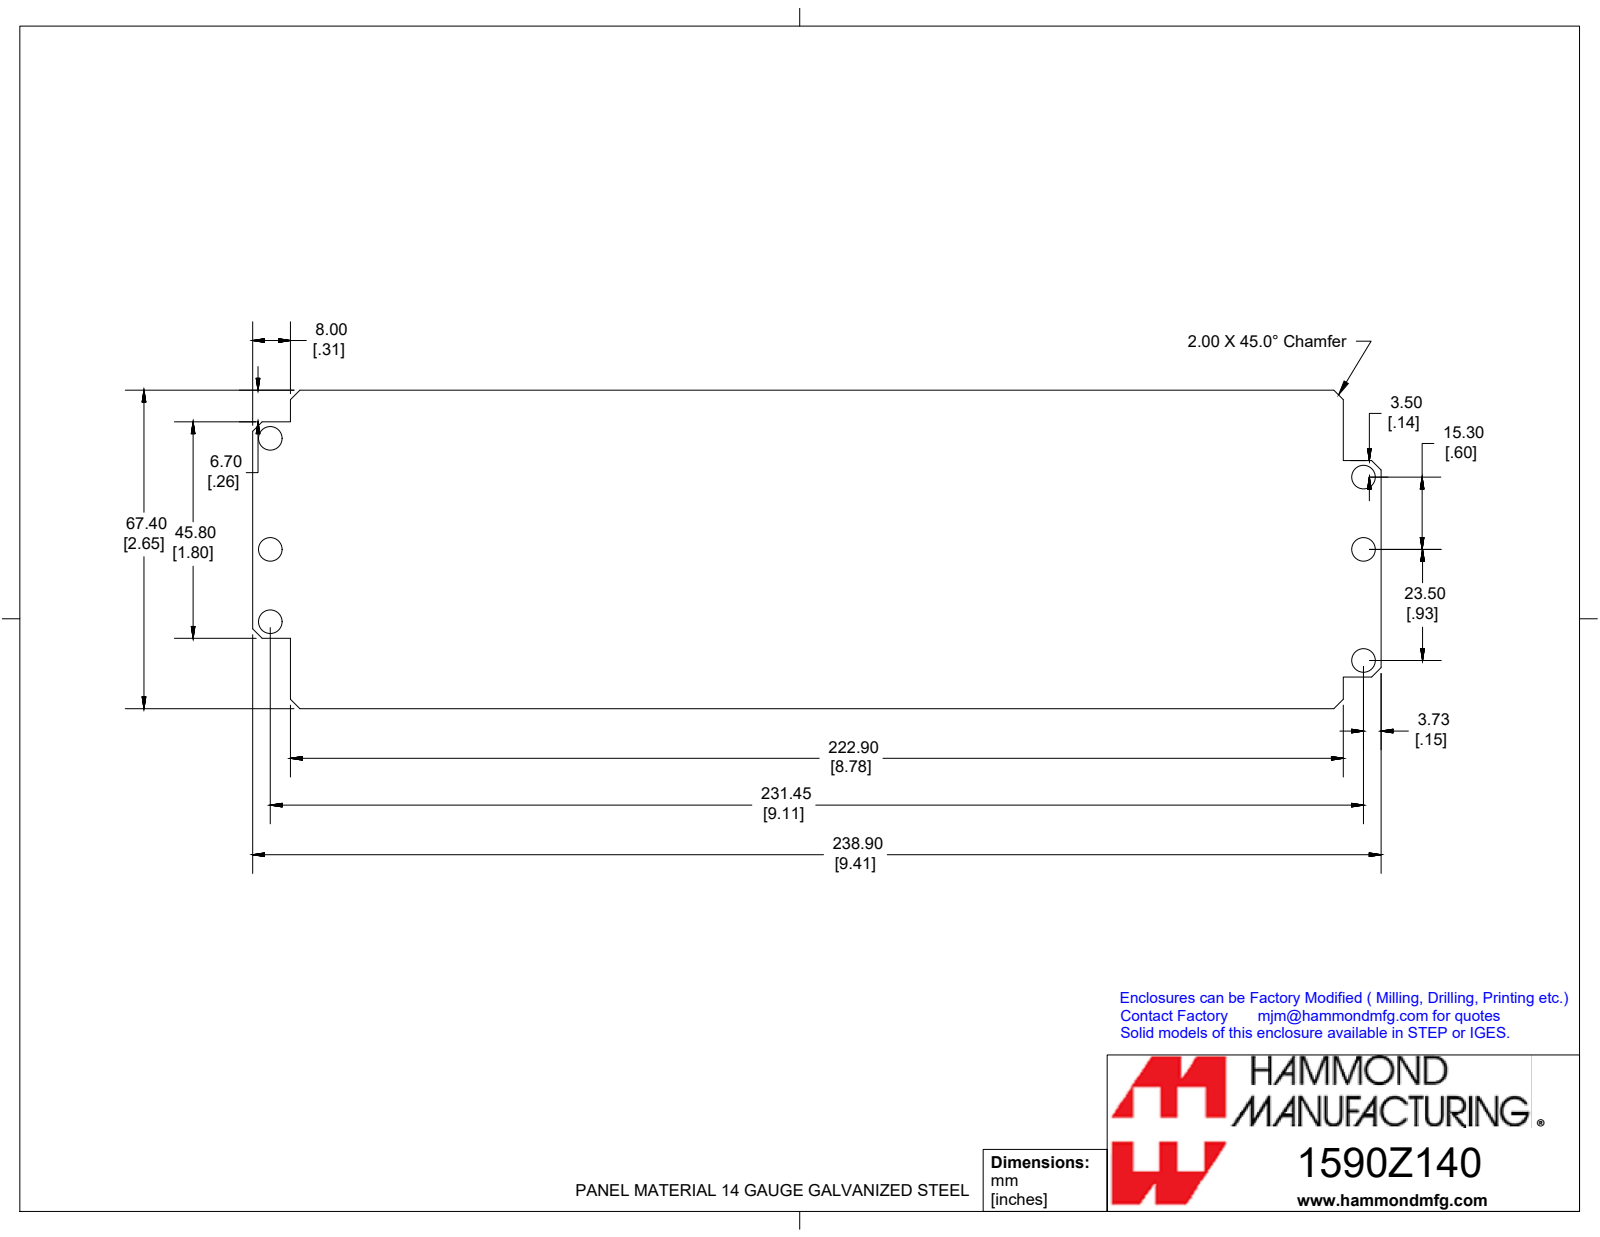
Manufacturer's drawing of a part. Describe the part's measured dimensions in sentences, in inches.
The part is named "1590Z140PL". Its 3-D file was written by "SolidWorks 2019 (CONFIG_CONTROL_DESIGN)". It is 1 solid with 28 faces: 22 planar, 6 cylindrical and 0 other. Overall it measures 9.406 by 2.654 by 0.064 inches. Its volume is 1.538 cubic inches and its surface area 50.17 square inches. Round holes: 6 of diameter 0.197. The main face-to-face distances are 0.063, 2.654, 9.406, 0.315, 9.091, 8.776, 0.264, 0.587, 2.067, 2.39. The hole center spacings are 0.602, 0.925, 1.528, 9.118, 9.132, 9.159, 9.112, 9.191.
